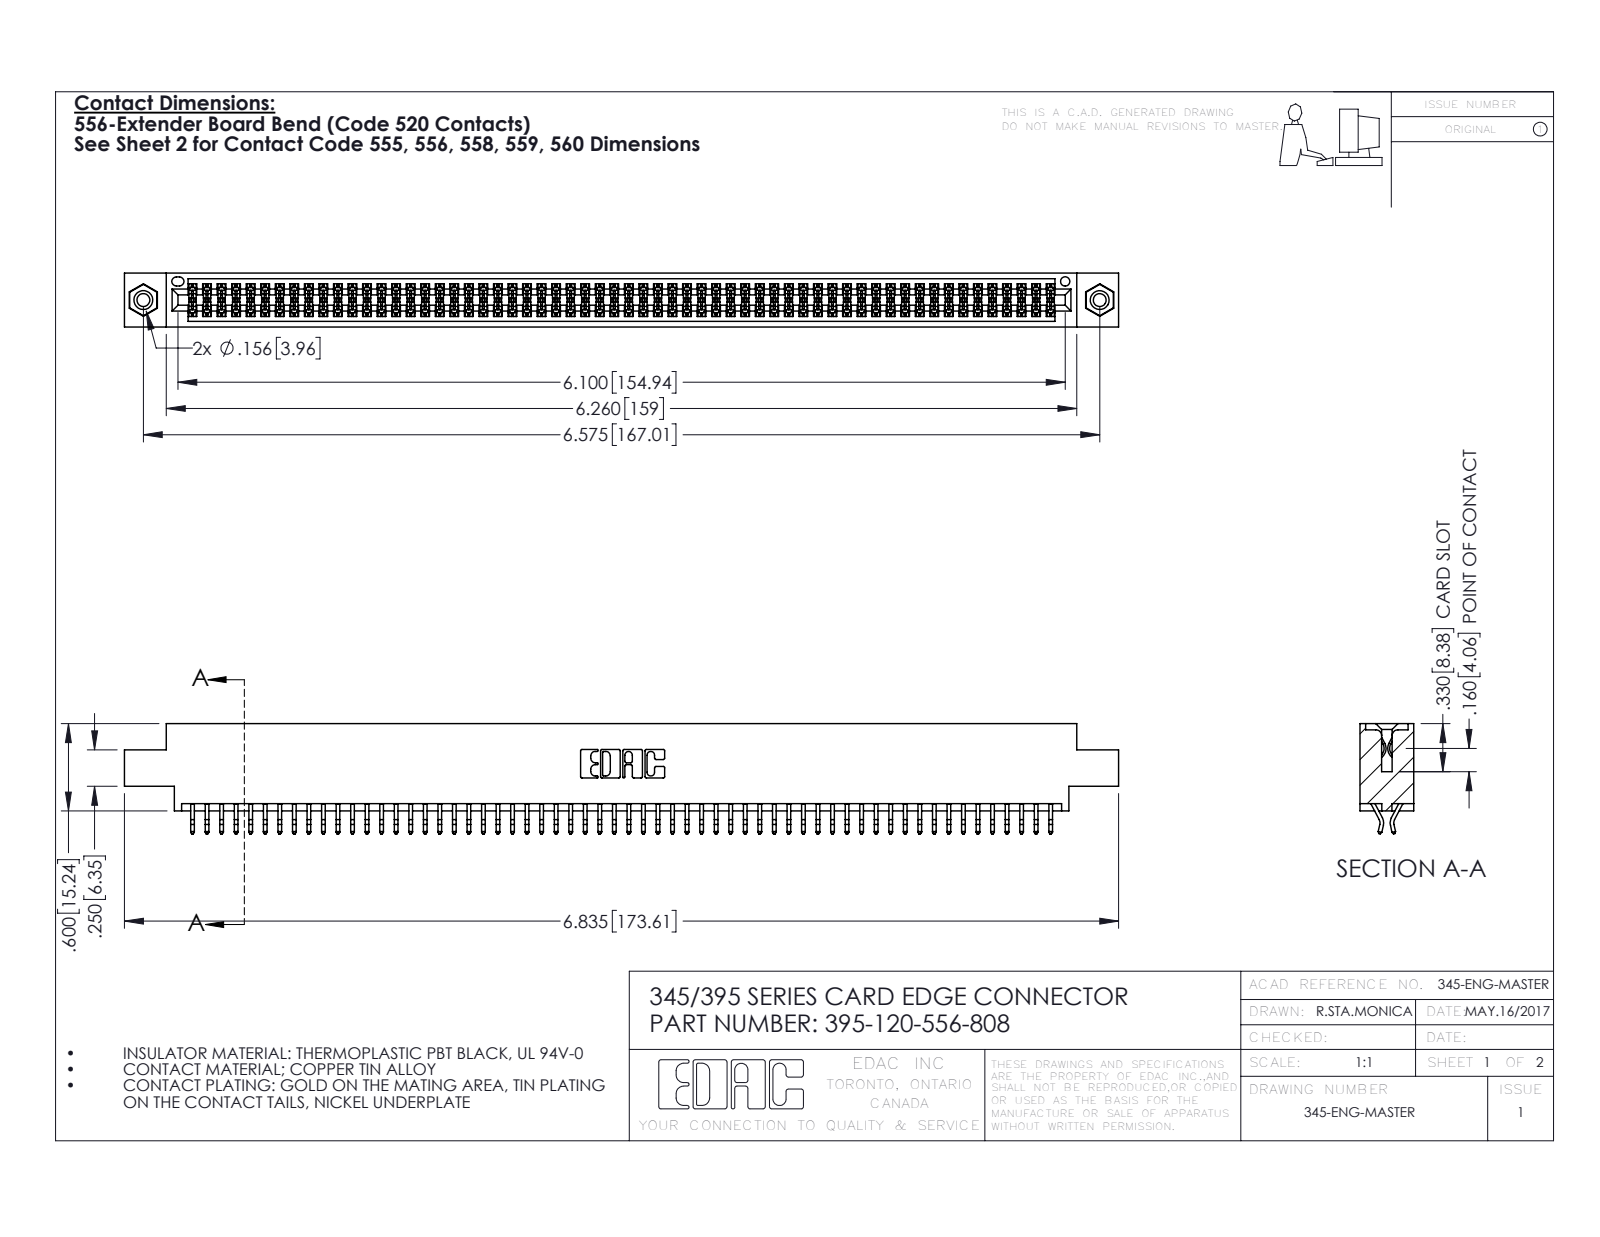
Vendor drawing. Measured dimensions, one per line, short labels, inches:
name: 345 Part_0.170 Offset - 0.156 Dia-TI; 345-292-001_556 Tail; 395-120-556-808; 345-250-001_345-250-003-102
written by: SolidWorks 2016 (CONFIG_CONTROL_DESIGN)
unit: in
bodies: 123 solids, 6910 faces (4556 planar, 2338 cylindrical, 16 other)
size: 6.835 × 0.757 × 0.37
volume: 1.032 in³; area: 39.36 in²
holes: 2× ⌀0.089, 2× ⌀0.125, 2× ⌀0.156, 1× ⌀0.064
bosses: 2× ⌀0.155
rounds: 180× R0.006, 22× R0.01, 6× R0.007, 6× R0.031, 3× R0.026, 2× R0.01, 2× R0.014, 2× R0.019
face distances: 0.072, 0.298, 0.37, 0.2, 0.025, 0.098, 0.272, 0.225, 0.175, 0.149
hole spacings: 0.27, 6.339, 6.575
